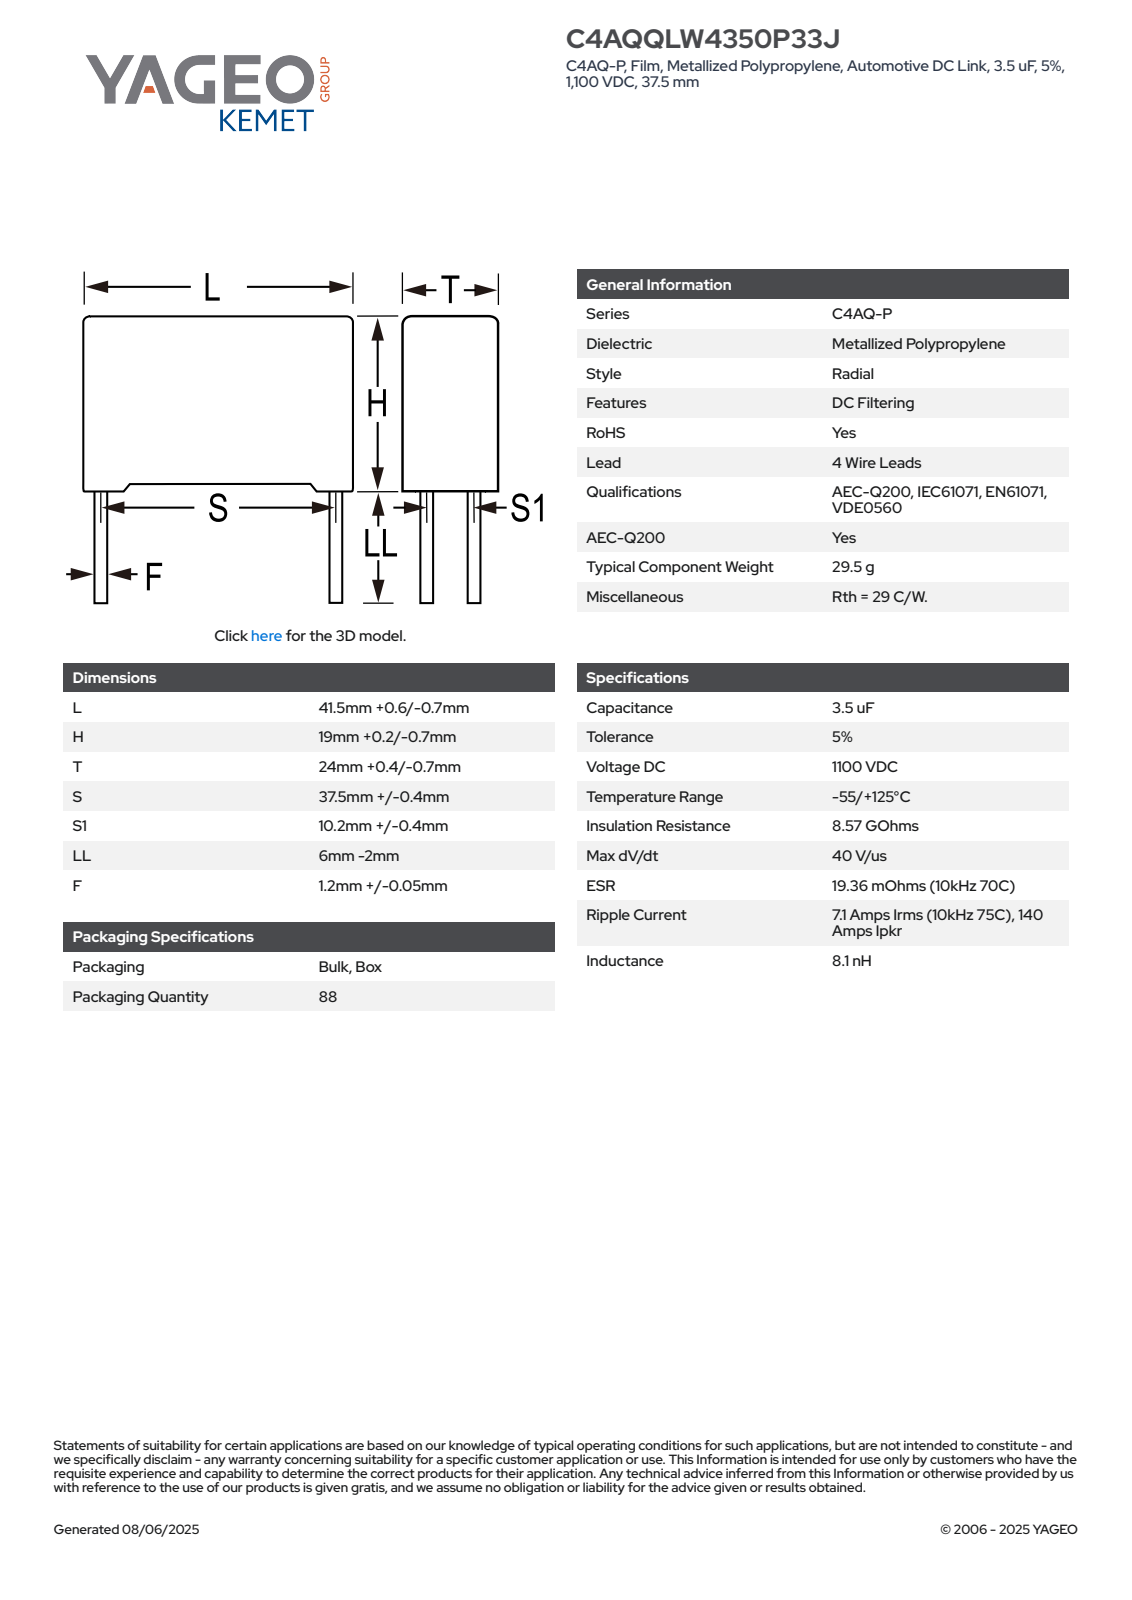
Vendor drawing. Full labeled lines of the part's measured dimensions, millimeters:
Part name (STEP PRODUCT): CFP_RB4_41.5X19X24_L42.1H19.2T24.4S37.5S110.2LL4F1.25
STEP written by: SolidWorks 2014 (AUTOMOTIVE_DESIGN)
Units: millimetres
Bodies: 4 solids, 87 faces (79 planar, 8 cylindrical, 0 other)
Overall size (bounding box): 42.1 × 24.41 × 23.2
Volume: 19 226 mm³ · Surface area: 4 801 mm²
Round bosses / shafts (diameter × count): ⌀1.25 ×4
Main face-to-face distances: 18.64, 24.4, 42.1, 0.56, 19.2, 24.41, 1.5, 40.6, 22.9, 39.1
